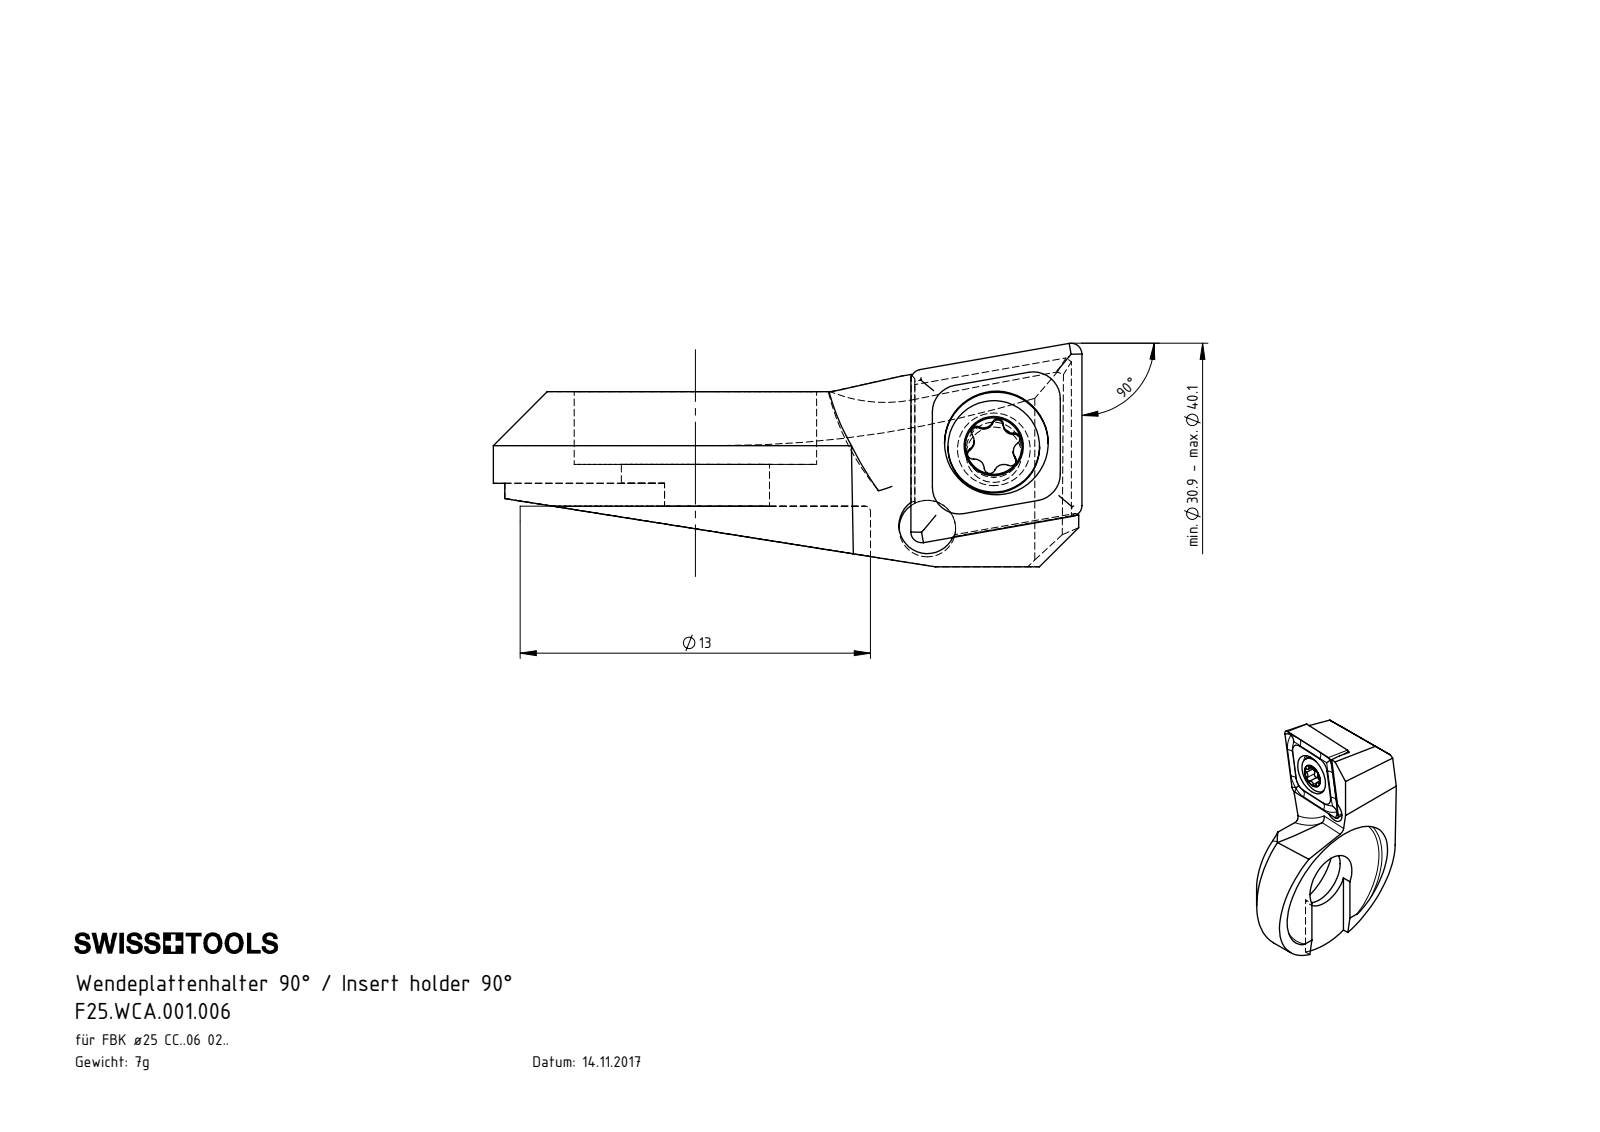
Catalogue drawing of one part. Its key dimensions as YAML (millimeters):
part_name: "CCMT060204; WCA-ER2.001.006_A; F25-WCA.001.006_C_fertigbearbeitet; F25.WCA.001.006"
step_written_by: "SolidWorks 2017 (CONFIG_CONTROL_DESIGN)"
units: millimeters
bodies: {solids: 5, faces: 147, planar: 48, cylindrical: 45, other: 54}
overall_size: [21.85, 15, 8.3]
volume: 874
surface_area: 1311
round_holes:
  - {diameter: 2.05, count: 1}
  - {diameter: 2.1, count: 1}
  - {diameter: 2.8, count: 1}
  - {diameter: 3.85, count: 1}
  - {diameter: 5.5, count: 1}
  - {diameter: 9, count: 1}
round_bosses_or_shafts:
  - {diameter: 3.4, count: 1}
  - {diameter: 2.5, count: 1}
partial_cylinders:
  - {radius: 0.21, count: 6}
  - {radius: 0.36, count: 5}
  - {radius: 0.5, count: 2}
  - {radius: 0.36, count: 1}
  - {radius: 1.05, count: 1}
  - {radius: 6.4, count: 1}
  - {radius: 6.5, count: 1}
  - {radius: 7.5, count: 1}
face_to_face_distances: [4.25, 4.15, 2.27, 2.7, 2.6, 1.55, 2.28, 3.4, 3.3, 0.7]
hole_center_spacings: [3.84, 3.99]
